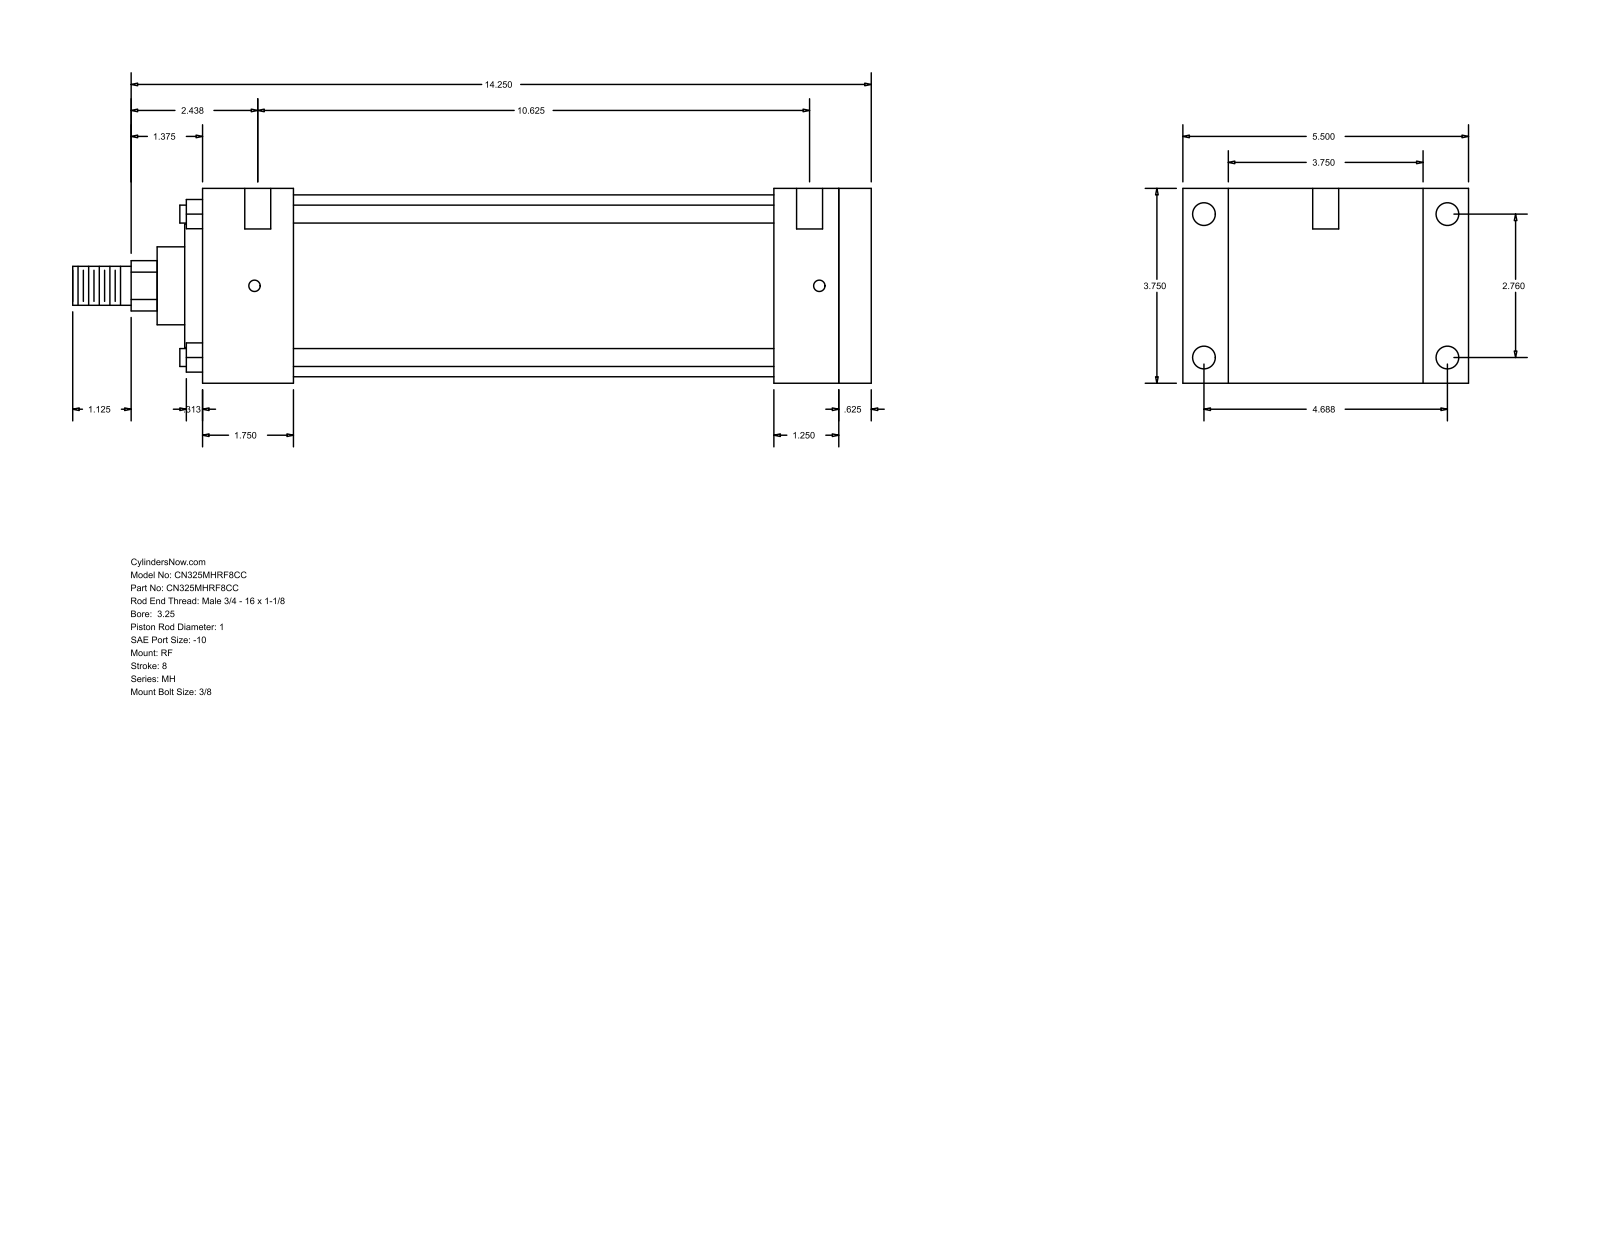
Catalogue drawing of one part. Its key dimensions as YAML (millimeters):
part_name: "MH_RF__0325_1"
step_written_by: "GSSL Pune (CONFIG_CONTROL_DESIGN)"
units: millimeters
bodies: {solids: 0, faces: 94, planar: 65, cylindrical: 29, other: 0}
overall_size: [390.52, 139.7, 95.25]
round_holes:
  - {diameter: 5.56, count: 4}
  - {diameter: 11.13, count: 4}
  - {diameter: 12.7, count: 2}
round_bosses_or_shafts:
  - {diameter: 8.76, count: 4}
  - {diameter: 88.9, count: 1}
  - {diameter: 60.33, count: 1}
  - {diameter: 38.1, count: 1}
  - {diameter: 25.4, count: 1}
  - {diameter: 19.05, count: 1}
partial_cylinders:
  - {radius: 12.29, count: 1}
face_to_face_distances: [95.24, 327.03, 311.15, 15.88, 22.23, 117.47, 44.46, 266.69, 282.57, 279.4]
hole_center_spacings: [70.1, 119.06, 138.16, 276.22, 1.58, 4.76, 269.88, 271.46]
